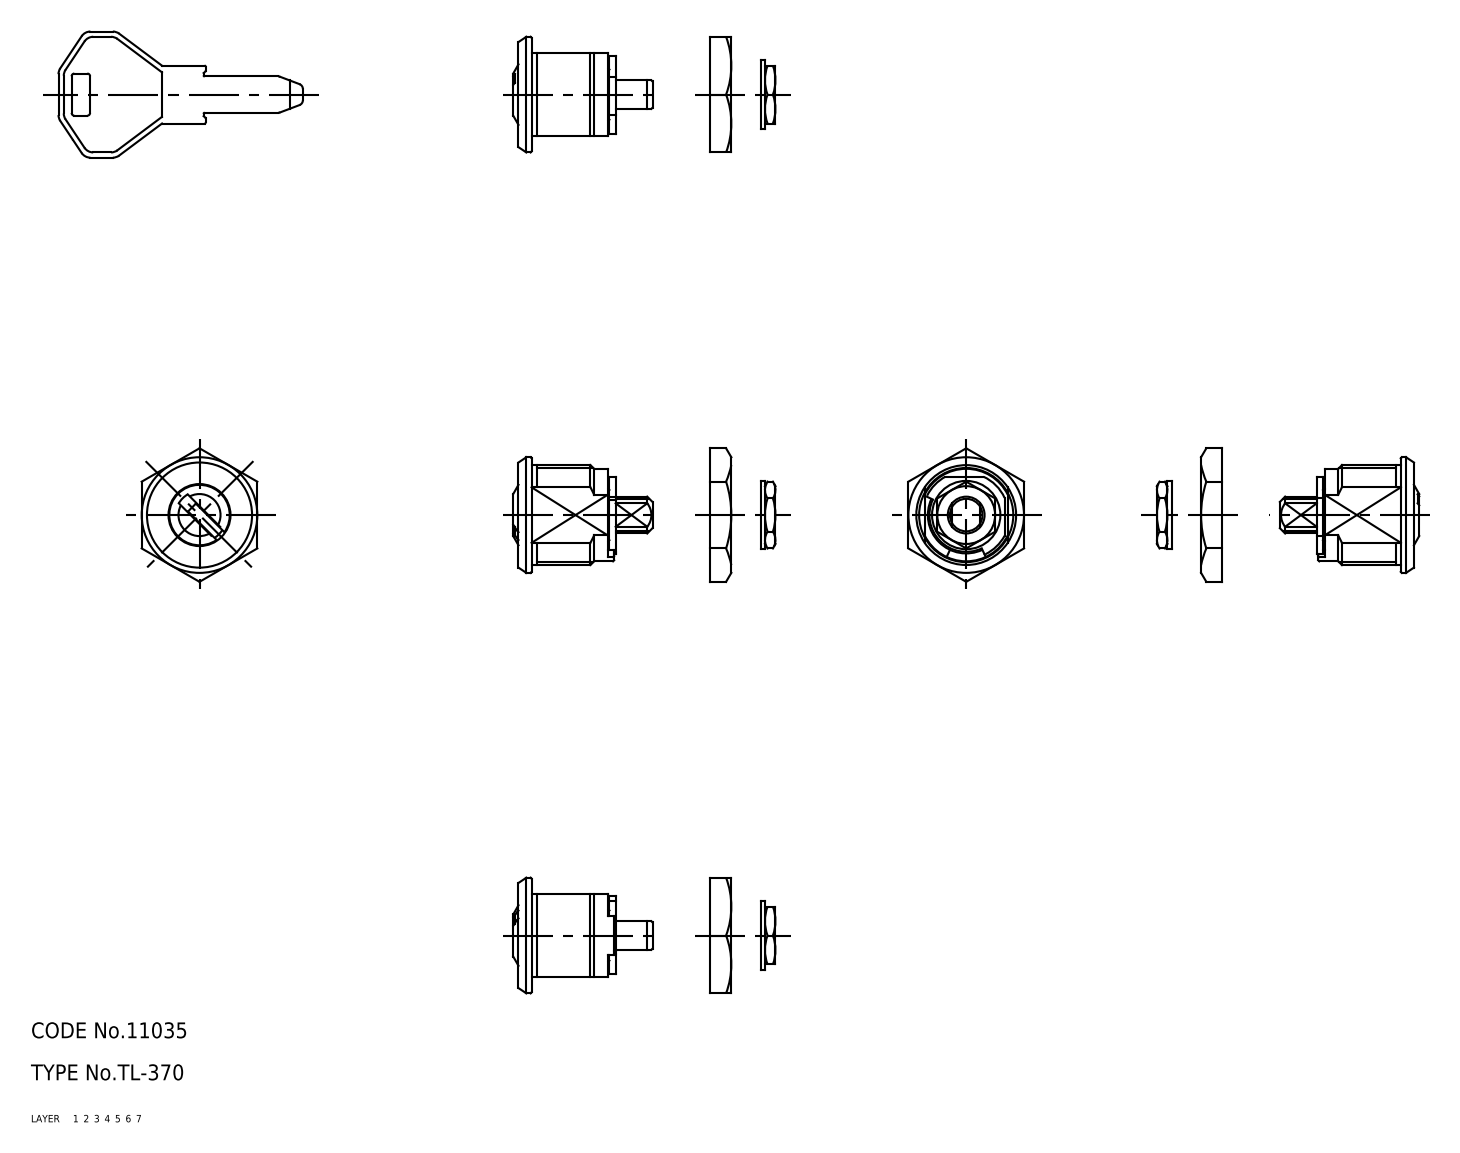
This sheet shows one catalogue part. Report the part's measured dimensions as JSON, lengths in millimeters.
{"part_name": "67118051; 67118064; 67118077; 67118090 (+2 more)", "step_written_by": "CADfix (AUTOMOTIVE_DESIGN)", "units": "millimeters", "bodies": {"solids": 6, "faces": 212, "planar": 0, "cylindrical": 0, "other": 212}, "overall_size": [113.02, 25.4, 22], "volume_mm3": 6757, "surface_area_mm2": 5160}
